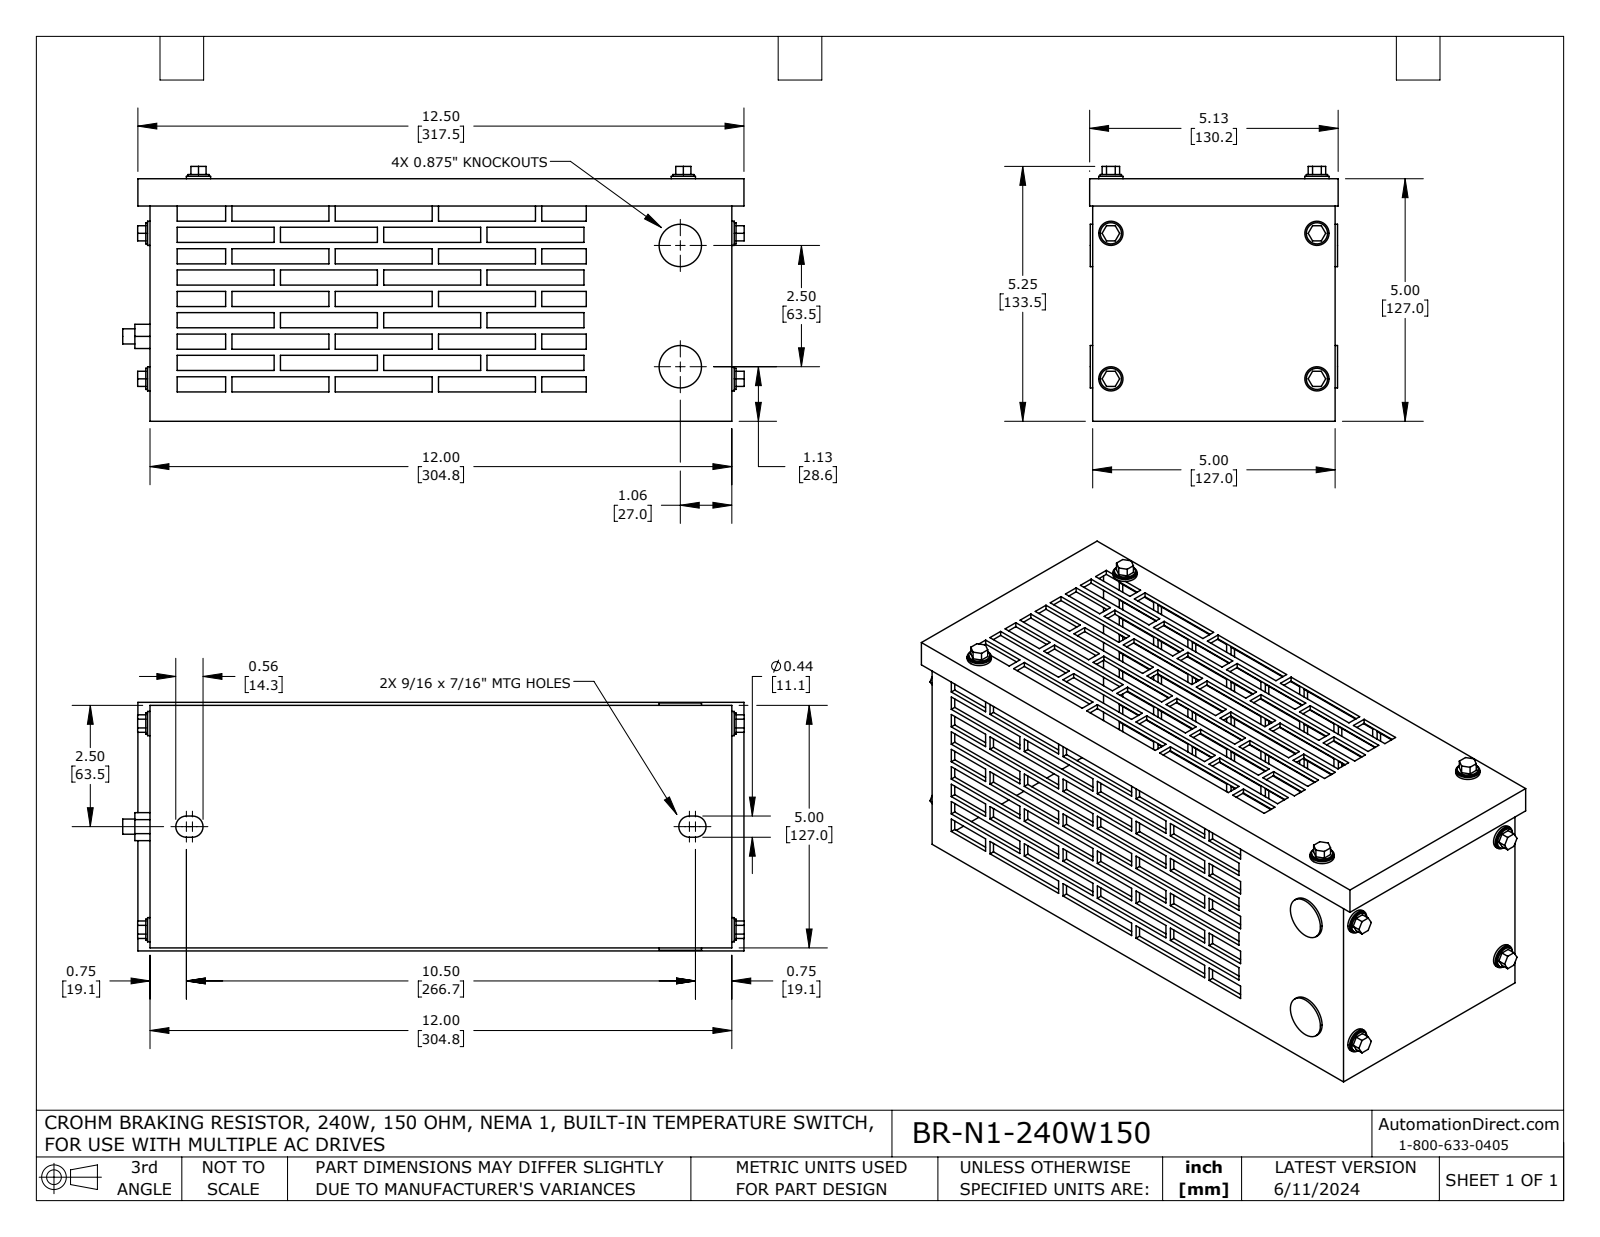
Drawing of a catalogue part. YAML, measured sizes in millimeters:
part_name: "BR-N1-240W150"
step_written_by: "SolidWorks 2021 (AUTOMOTIVE_DESIGN)"
units: millimeters
bodies: {solids: 30, faces: 753, planar: 659, cylindrical: 94, other: 0}
overall_size: [325.6, 133.5, 130.2]
volume: 370300
surface_area: 330100
round_holes:
  - {diameter: 6.4, count: 8}
  - {diameter: 19.1, count: 2}
round_bosses_or_shafts:
  - {diameter: 12.7, count: 8}
  - {diameter: 11.1, count: 8}
  - {diameter: 22.2, count: 2}
  - {diameter: 8, count: 1}
partial_cylinders:
  - {radius: 5.6, count: 4}
face_to_face_distances: [2.5, 124.5, 127, 121.9, 302.3, 1.6, 126.1, 304.8, 299.7, 22.4]
hole_center_spacings: [108, 76.2, 132.1, 254, 276, 63.5]
